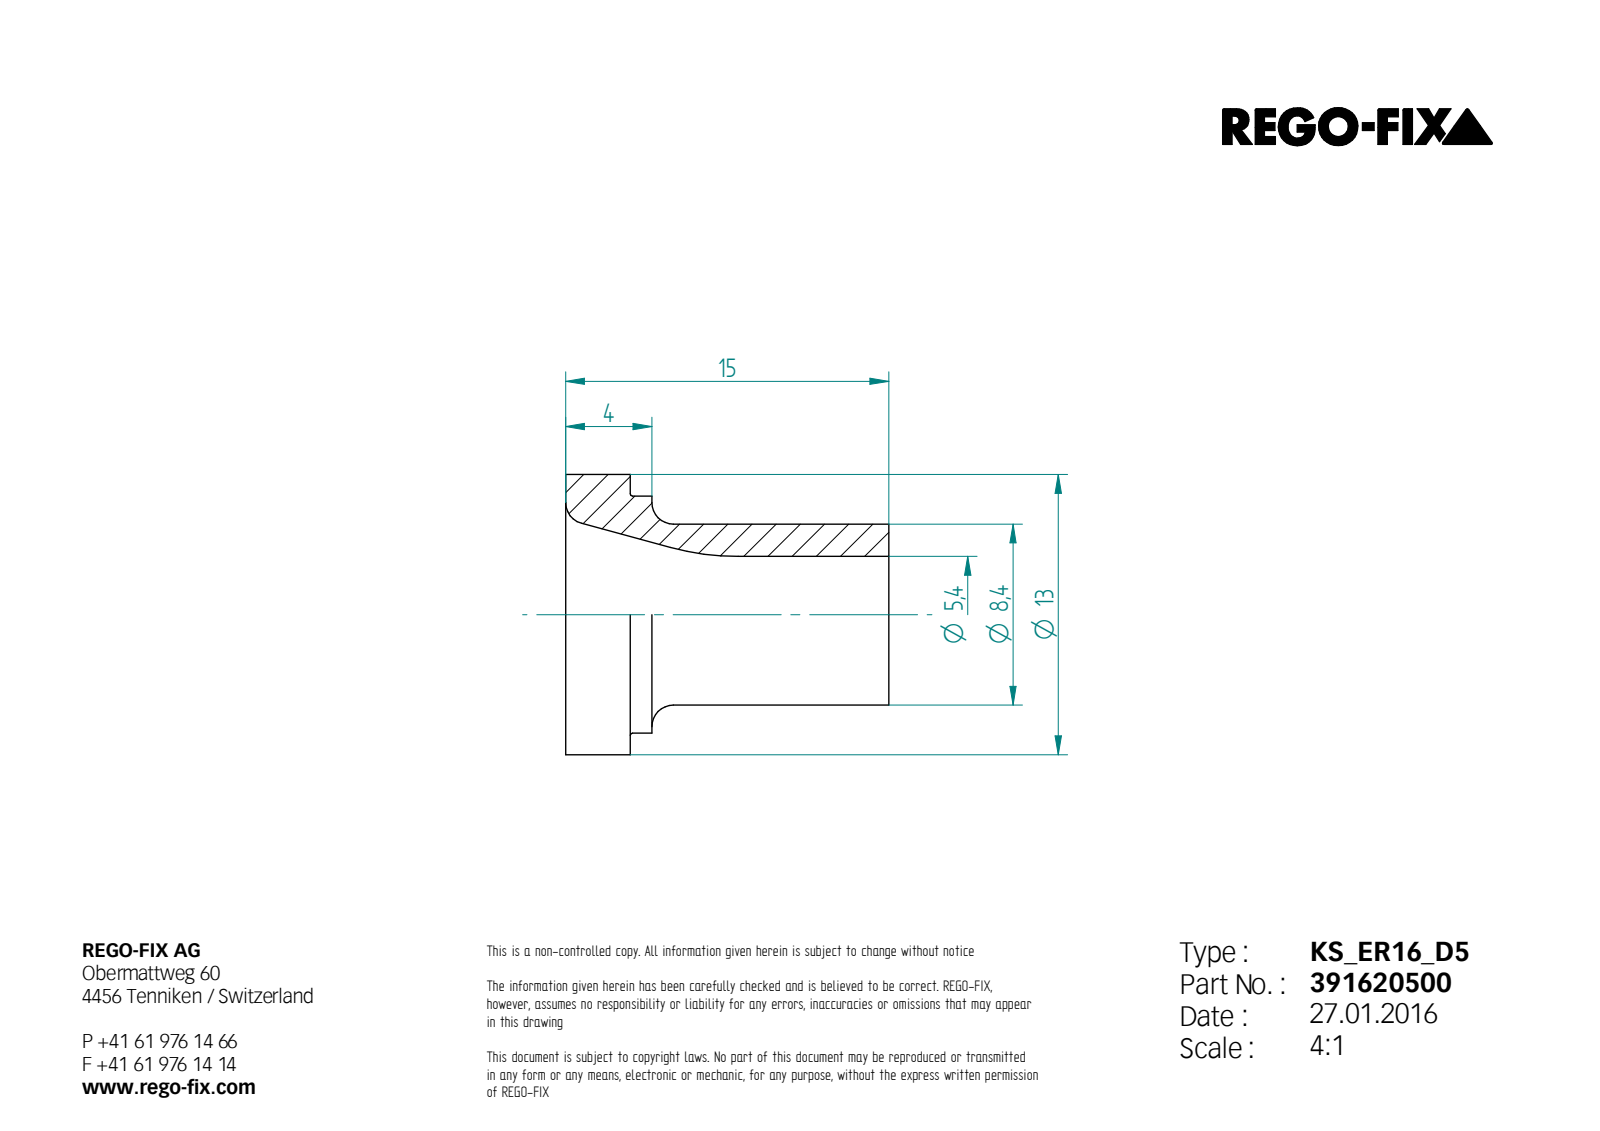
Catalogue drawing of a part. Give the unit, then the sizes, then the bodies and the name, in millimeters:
Units: millimetres
Overall size (bounding box): 15 × 13 × 13
Round holes (diameter × count): ⌀5.4 ×1
Round bosses / shafts (diameter × count): ⌀13 ×1, ⌀11 ×1, ⌀8.4 ×1
Main face-to-face distances: 3, 15, 12, 4, 1, 11
Volume: 646 mm³ · Surface area: 905 mm²
Bodies: 1 solid, 13 faces (4 planar, 4 cylindrical, 5 other)
STEP written by: Unknown (AUTOMOTIVE_DESIGN)
